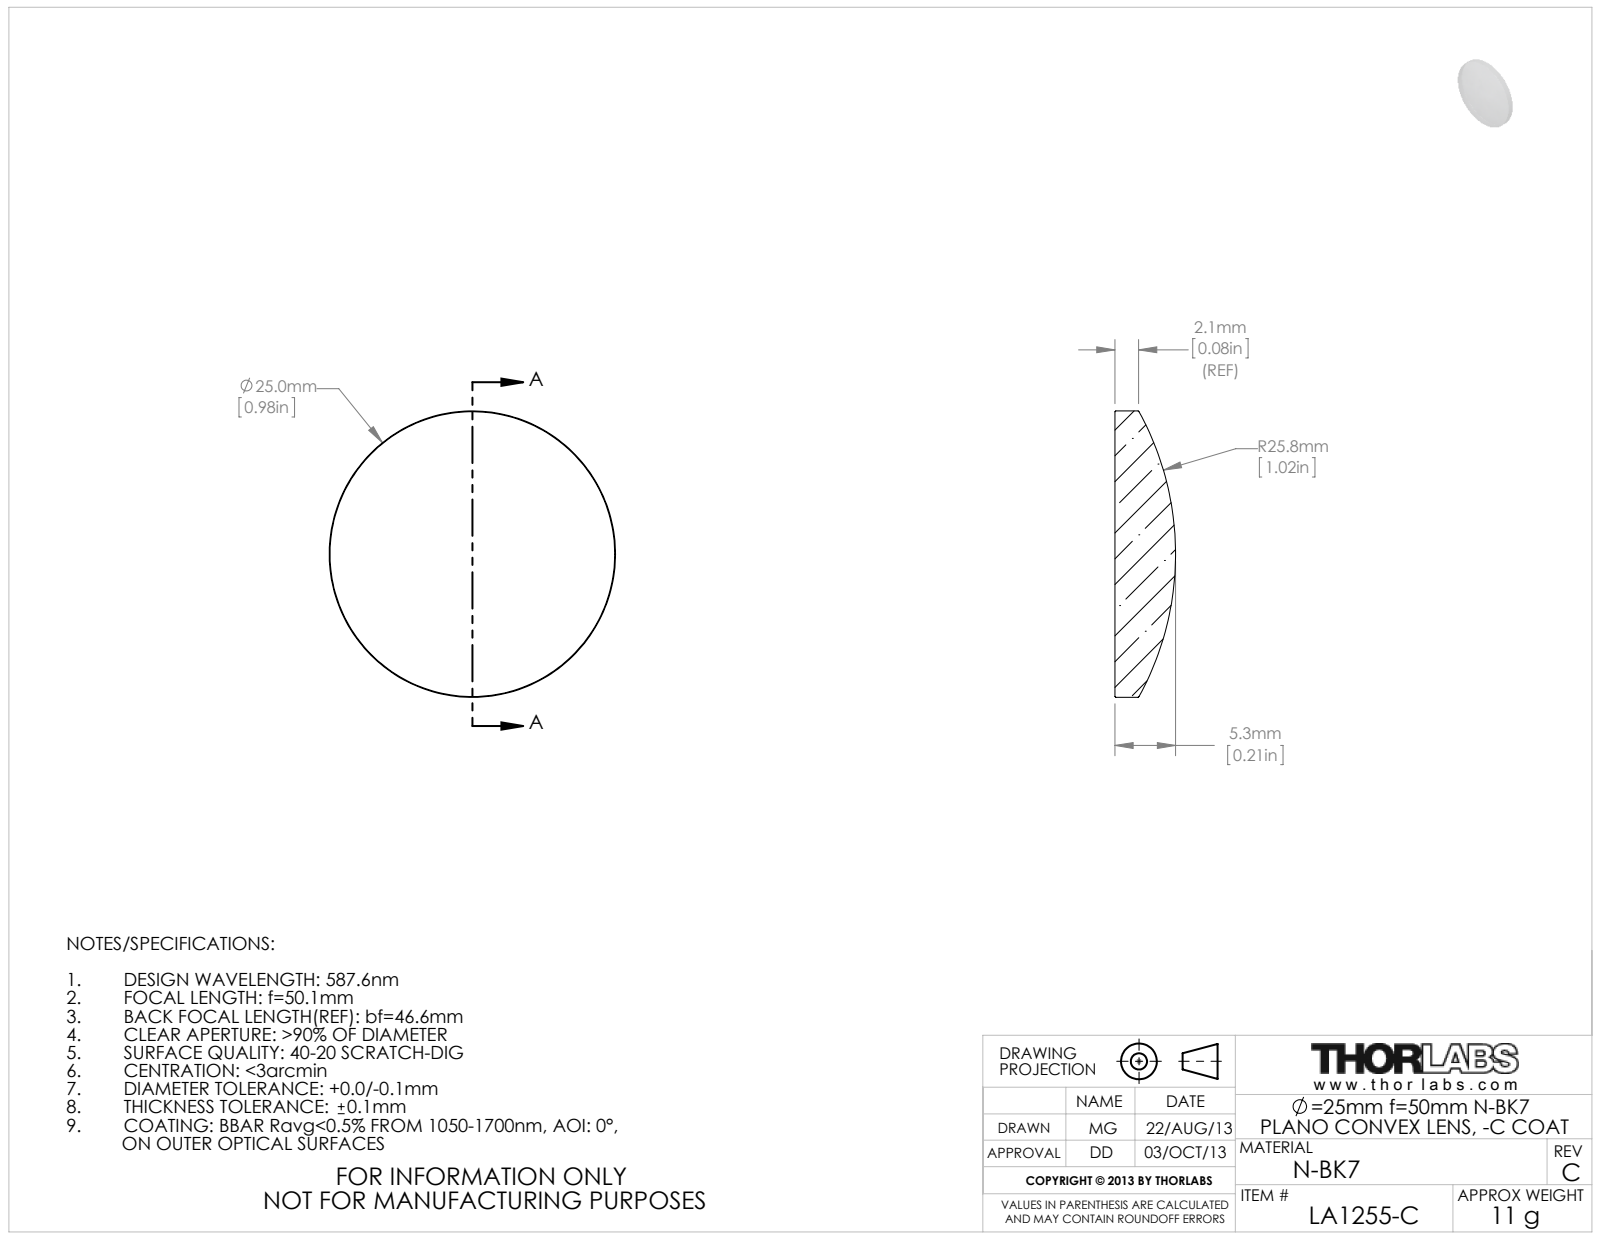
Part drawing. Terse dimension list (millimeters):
name: 19050-E0W
written by: SolidWorks 2009 (AUTOMOTIVE_DESIGN)
unit: mm
bodies: 1 solid, 5 faces (1 planar, 2 cylindrical, 2 other)
size: 25 × 25 × 5.3
volume: 1 826 mm³; area: 1 177 mm²
bosses: 1× ⌀25
